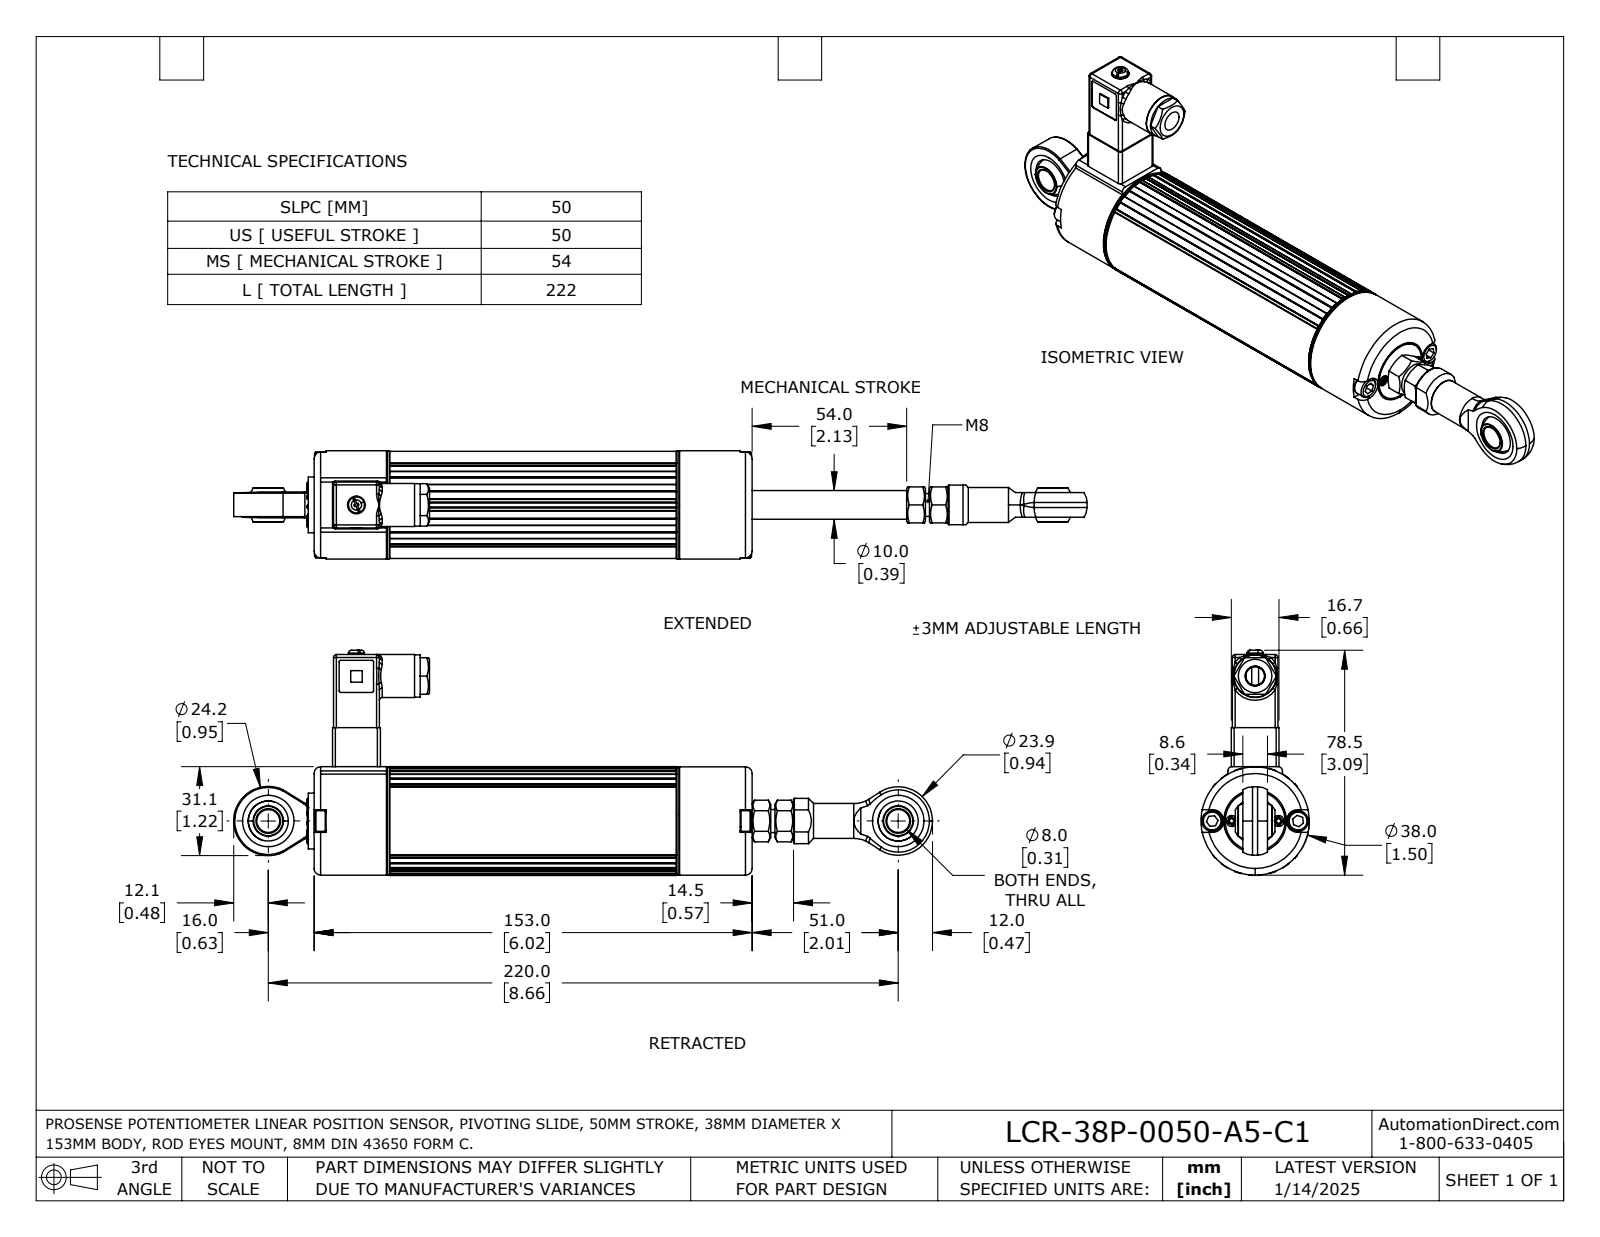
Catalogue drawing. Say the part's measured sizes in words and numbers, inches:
The part is named "LCR-38P-0050-A5-C1". Its 3-D file was written by "SolidWorks 2023 (AUTOMOTIVE_DESIGN)". It is 10 solids with 657 faces: 295 planar, 208 cylindrical and 154 other. Overall it measures 9.608 by 3.093 by 1.488 inches. Its volume is 11.67 cubic inches and its surface area 72.84 square inches. Round holes: 6 of diameter 0.102, 4 of diameter 0.091, 3 of diameter 0.315, 3 of diameter 0.551, 2 of diameter 0.094, 2 of diameter 0.1, 2 of diameter 0.111, 2 of diameter 0.134, 2 of diameter 0.152, 2 of diameter 0.165, 1 of diameter 0.079, 1 of diameter 0.118. Round bosses or shafts: 6 of diameter 0.063, 4 of diameter 0.283, 4 of diameter 0.15, 2 of diameter 0.48, 2 of diameter 0.079, 1 of diameter 1.488, 1 of diameter 0.823, 1 of diameter 0.768. Partial cylindrical surfaces (rounded edges, fillets, slot ends): 32 of radius 0.008, 20 of radius 0.039, 14 of radius 0.02, 6 of radius 0.016, 2 of radius 0.012, 2 of radius 0.059, 2 of radius 0.083, 2 of radius 0.098. The main face-to-face distances are 3.937, 1.043, 4.98, 0.031, 0.045, 0.612, 0.598, 0.014, 0.644, 0.138. The hole center spacings are 0.632, 0.075, 0.634, 1.258, 0.264, 0.268, 0.294, 0.323.
